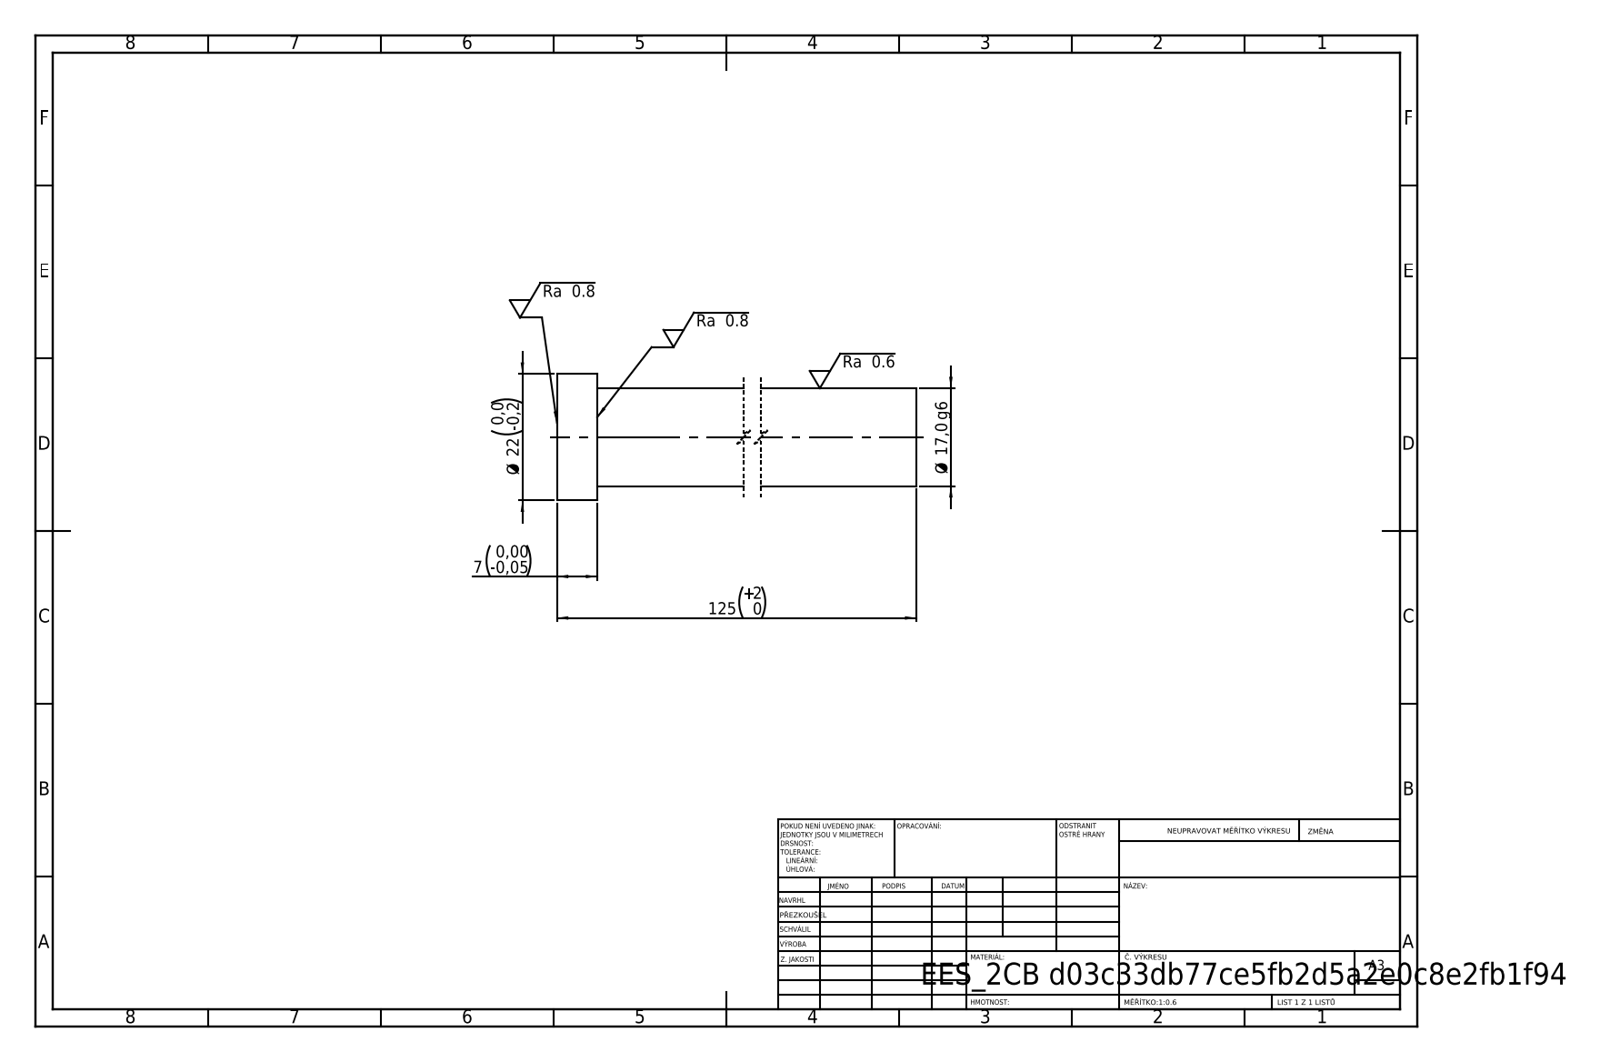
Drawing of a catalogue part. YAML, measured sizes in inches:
step_written_by: "SolidWorks 2019 (CONFIG_CONTROL_DESIGN)"
units: inches
bodies: {solids: 1, faces: 7, planar: 3, cylindrical: 4, other: 0}
overall_size: [4.921, 0.866, 0.866]
volume: 1.797
surface_area: 11.7
round_bosses_or_shafts:
  - {diameter: 0.866, count: 1}
  - {diameter: 0.669, count: 1}
face_to_face_distances: [4.921, 0.276, 4.646]
